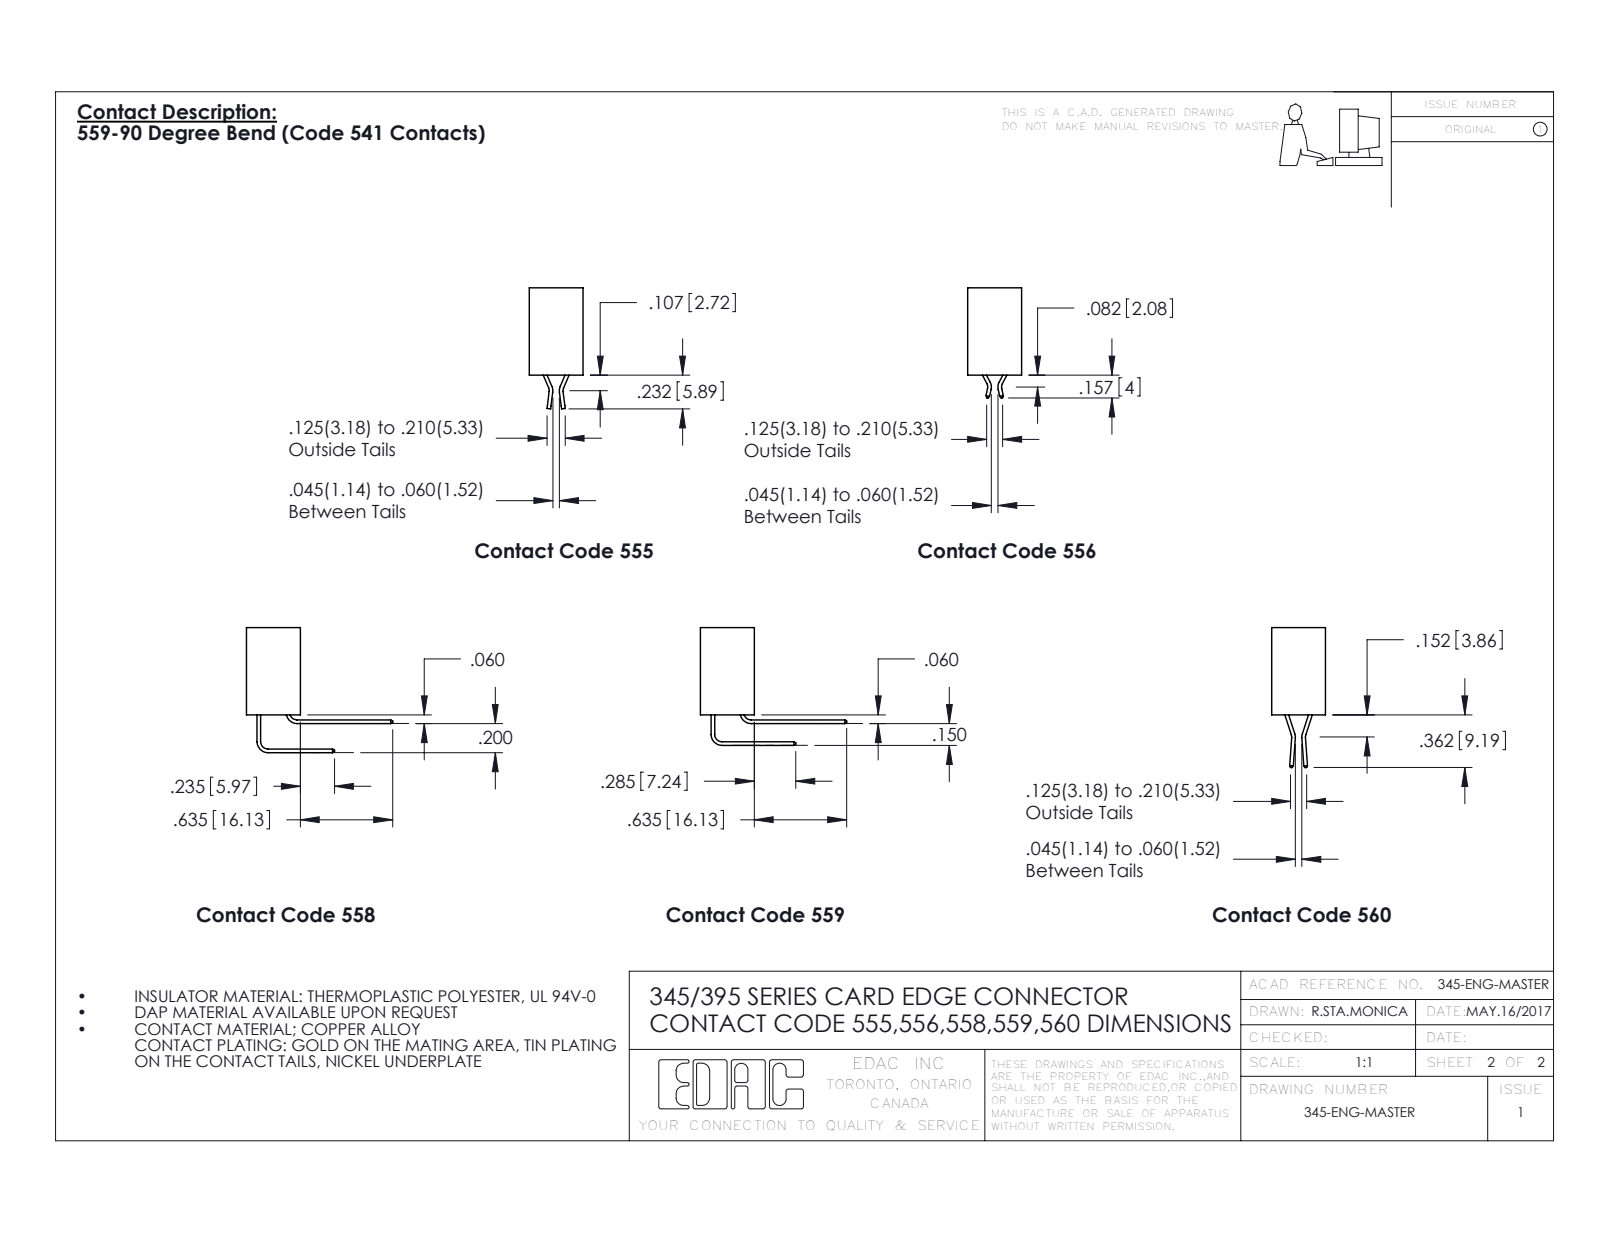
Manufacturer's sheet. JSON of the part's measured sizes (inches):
{"part_name": "395-010-559-412; 345-292-001_558 559 Tail - 1; 345 Part_0.110 Offset - Side Mount", "step_written_by": "SolidWorks 2016 (CONFIG_CONTROL_DESIGN)", "units": "inches", "bodies": {"solids": 11, "faces": 730, "planar": 504, "cylindrical": 226, "other": 0}, "overall_size": [1.835, 1.005, 0.659], "volume_in3": 0.246, "surface_area_in2": 7.853, "round_holes": [[0.128, 2], [0.064, 1]], "partial_cylinders_radius": [[0.01, 22], [0.006, 20], [0.007, 6], [0.031, 6], [0.026, 3], [0.031, 2], [0.04, 2], [0.014, 1]], "face_to_face_distances": [0.2, 0.072, 0.298, 0.37, 0.1, 0.6, 0.098, 0.272, 0.025, 0.06], "hole_center_spacings": [1.575]}
